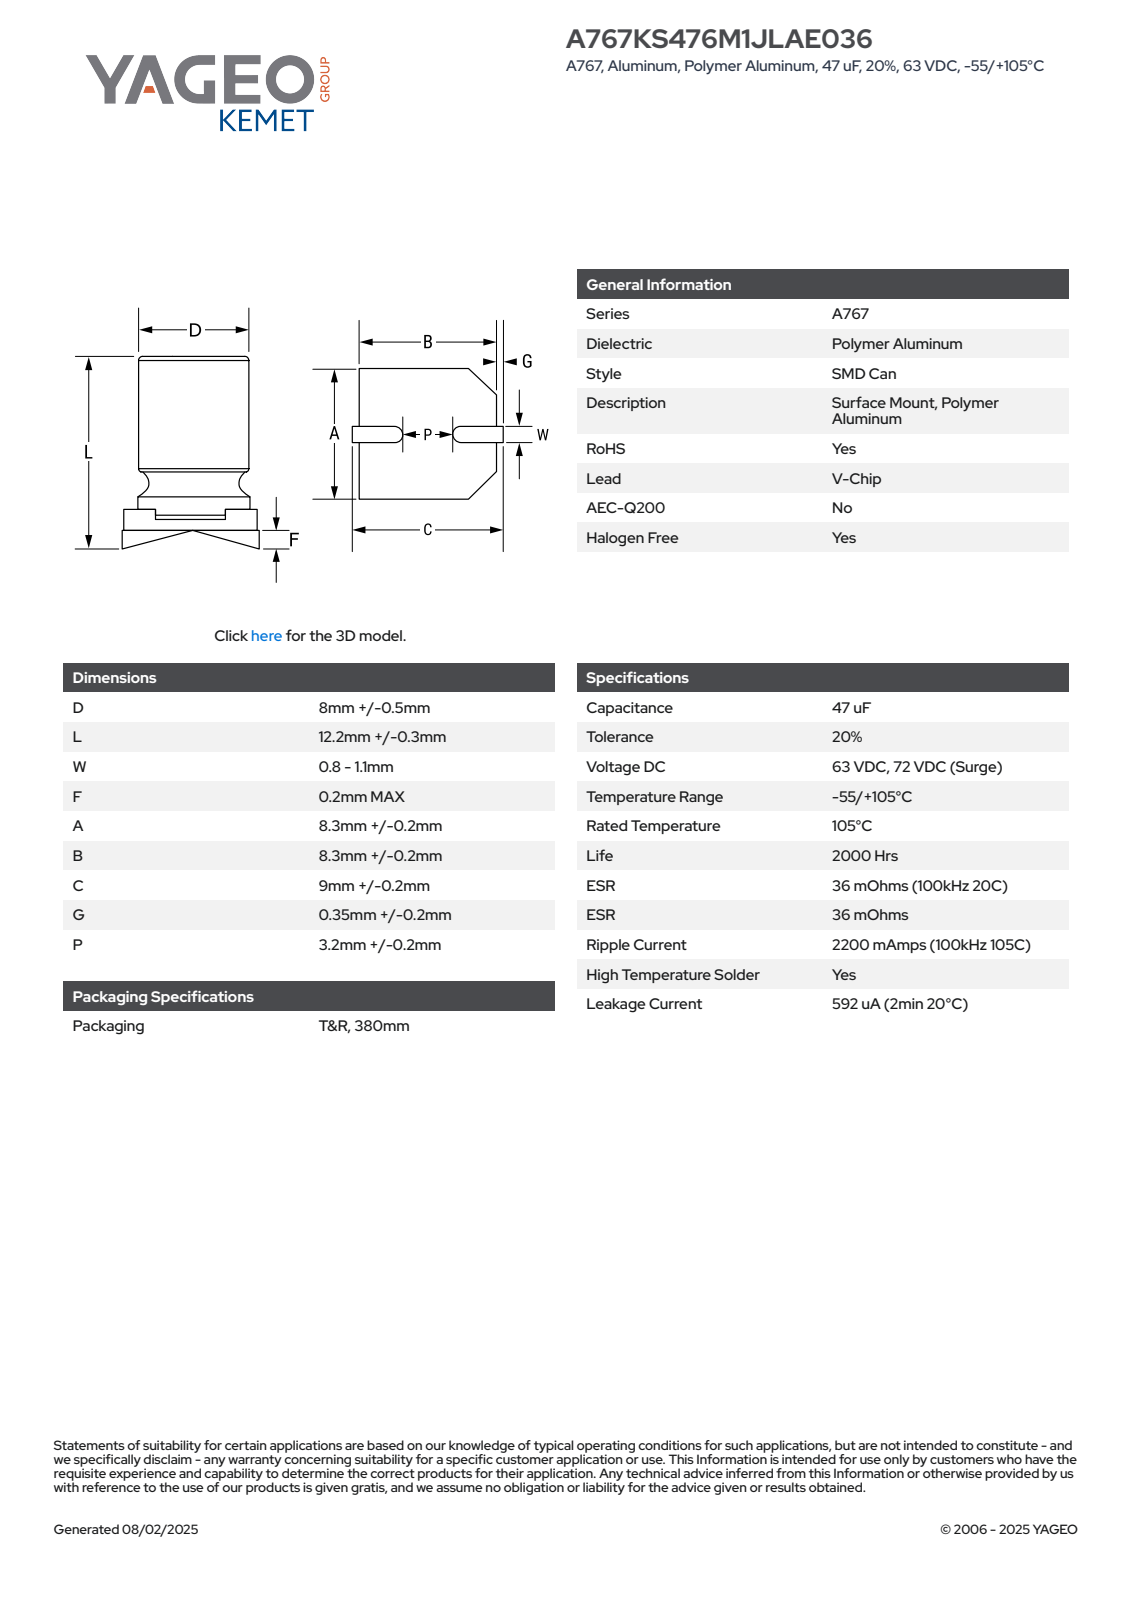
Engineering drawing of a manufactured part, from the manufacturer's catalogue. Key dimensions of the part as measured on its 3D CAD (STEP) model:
Part name (STEP PRODUCT): CAC_KS_8X12.2_D8.5L12.5W1.1F0.2A8.5B8.5C9.2P3.4
STEP written by: SolidWorks 2021 (AUTOMOTIVE_DESIGN)
Units: millimetres
Bodies: 5 solids, 76 faces (59 planar, 11 cylindrical, 6 other)
Overall size (bounding box): 12.51 × 9.2 × 8.5
Volume: 661 mm³ · Surface area: 644 mm²
Round bosses / shafts (diameter × count): ⌀8.13 ×1
Partial cylindrical surfaces — rounded edges, fillets, slot ends (radius × count): R0.2 ×2, R3.38 ×1, R4.25 ×1
Main face-to-face distances: 0.63, 12.3, 11.67, 12.31, 11.68, 8.5, 3.12, 2.49, 9.18, 9.19
